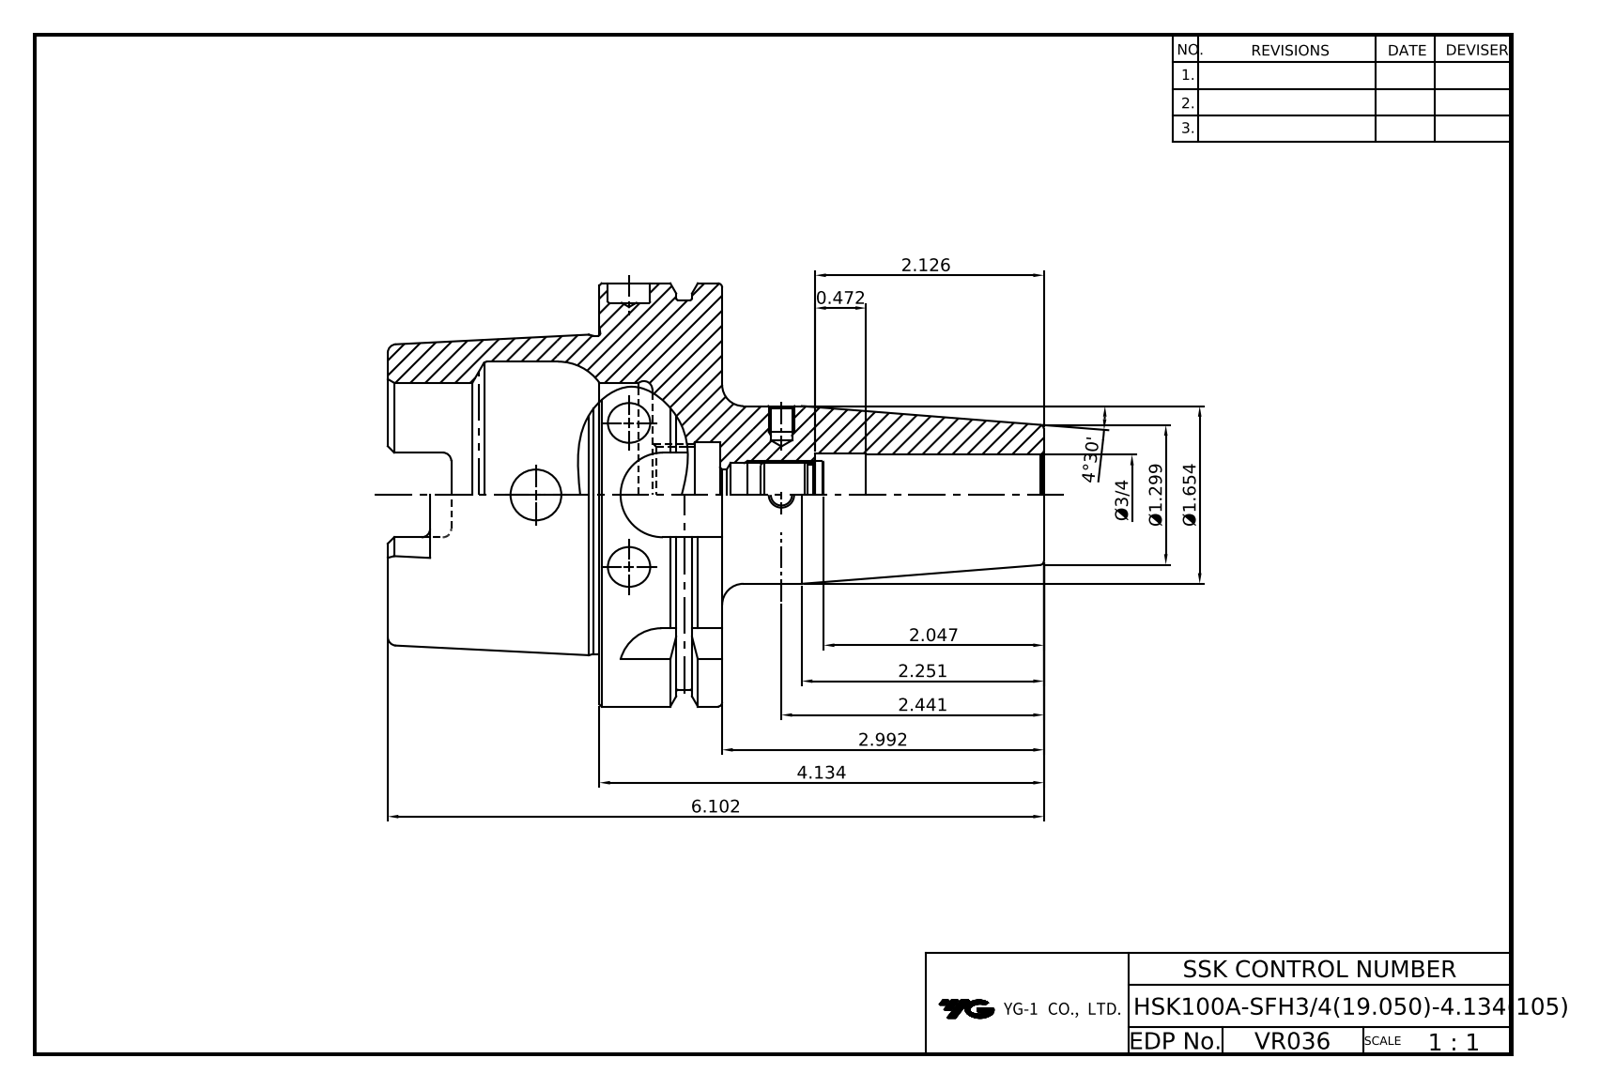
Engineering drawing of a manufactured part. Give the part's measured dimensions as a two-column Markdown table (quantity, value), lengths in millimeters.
| quantity | value |
| --- | --- |
| part name | HSK100A_SFH19_05_105 |
| STEP written by | CREO PARAMETRIC BY PTC INC, 2018400 (CONFIG_CONTROL_DESIGN) |
| units | millimeters |
| bodies | 1 solid, 207 faces (55 planar, 68 cylindrical, 84 other) |
| overall size | 155 × 100 × 100 |
| volume | 321 452 mm³ |
| surface area | 64 486 mm² |
| round holes (diameter × count) | 5 × 2, 6 × 2, 12 × 2, 10 × 1, 15.1 × 1, 19.05 × 1, 19.65 × 1, 22.5 × 1, 24 × 1, 25 × 1, 53 × 1, 63.96 × 1 |
| round bosses / shafts (diameter × count) | 100 × 1, 92 × 1, 75.16 × 1, 42 × 1 |
| partial cylindrical surfaces (radius × count) | 2 × 6, 4.88 × 4, 10 × 4 |
| main face-to-face distances | 29, 12.5, 16.5, 62.5, 50, 79, 10, 22.5, 72.5, 6.5 |
| hole center spacings | 36, 58 |
